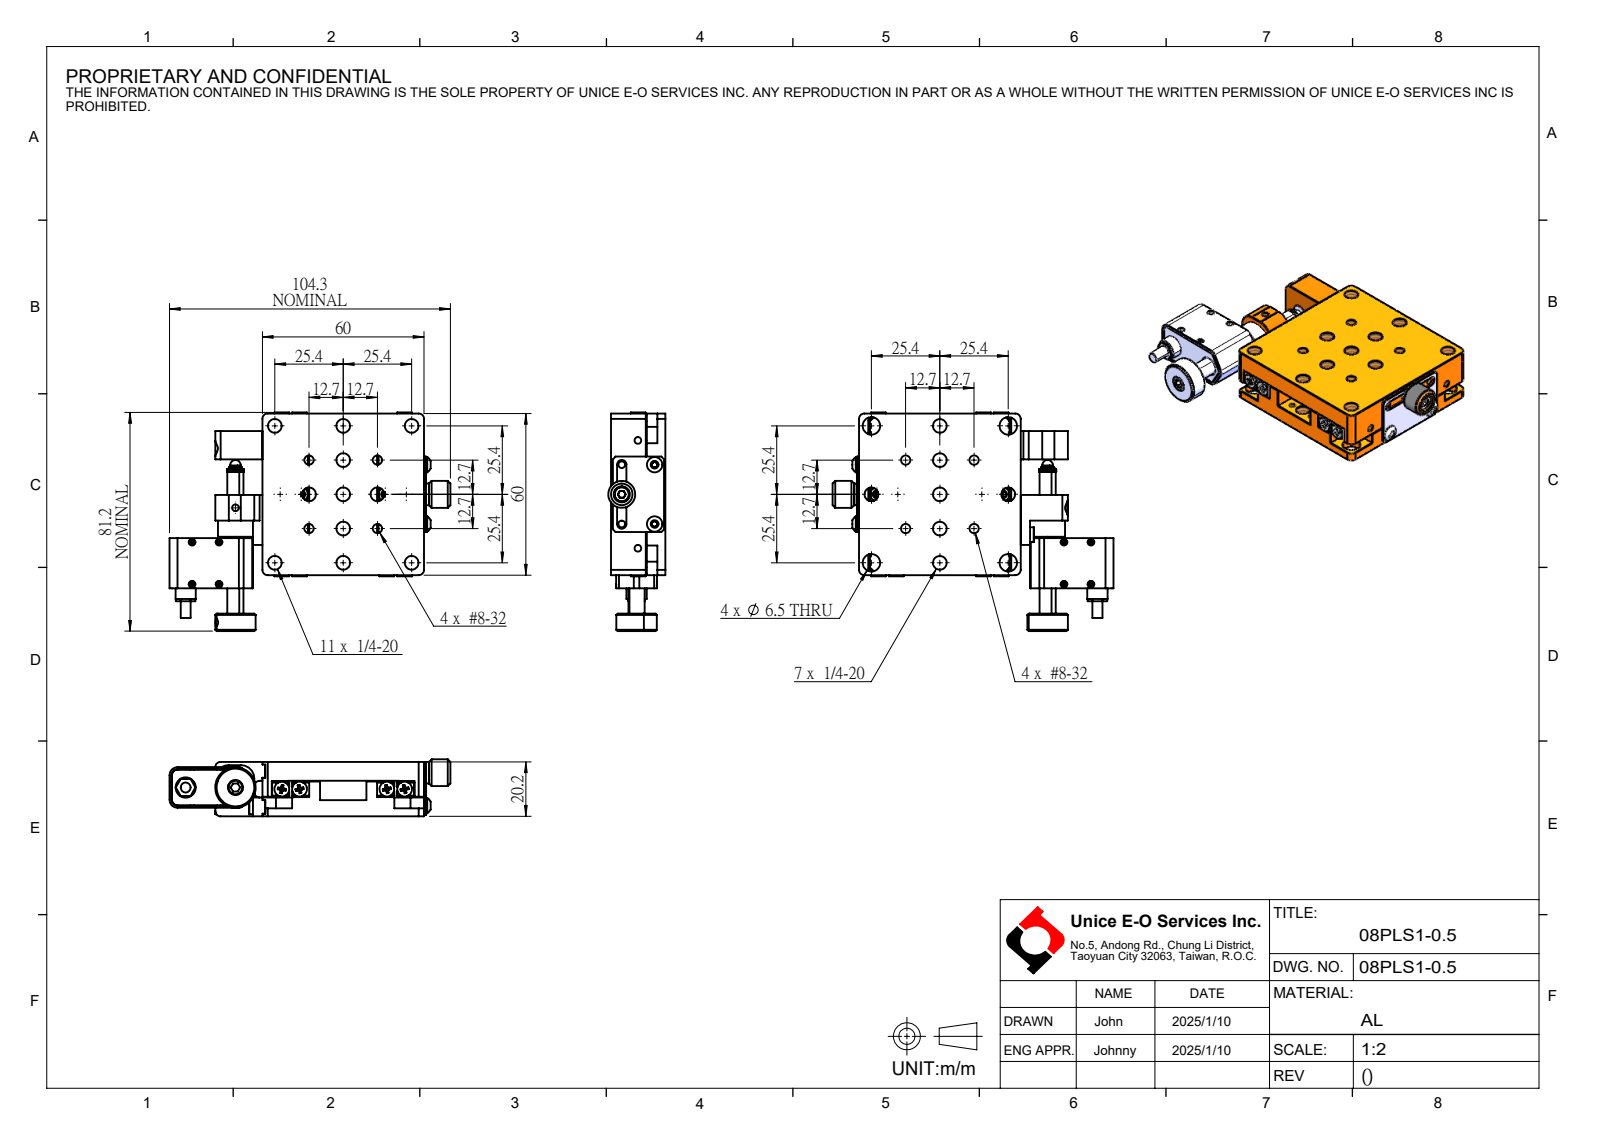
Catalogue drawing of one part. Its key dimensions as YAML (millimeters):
part_name: "08PLS1-0.5"
step_written_by: "SolidWorks 2024 (CONFIG_CONTROL_DESIGN)"
units: millimeters
bodies: {solids: 0, faces: 1785, planar: 652, cylindrical: 504, other: 629}
overall_size: [104.3, 81.17, 21.2]
round_holes:
  - {diameter: 2.05, count: 20}
  - {diameter: 2.5, count: 18}
  - {diameter: 3, count: 13}
  - {diameter: 5, count: 13}
  - {diameter: 5.11, count: 13}
  - {diameter: 6.5, count: 7}
  - {diameter: 3.45, count: 4}
  - {diameter: 3.4, count: 3}
  - {diameter: 1.4, count: 2}
  - {diameter: 2, count: 2}
  - {diameter: 3.2, count: 2}
  - {diameter: 3.5, count: 2}
round_bosses_or_shafts:
  - {diameter: 3, count: 9}
  - {diameter: 5.5, count: 8}
  - {diameter: 6, count: 3}
  - {diameter: 5.7, count: 2}
  - {diameter: 2, count: 2}
  - {diameter: 1.4, count: 2}
  - {diameter: 15, count: 1}
  - {diameter: 10, count: 1}
partial_cylinders:
  - {radius: 2, count: 11}
  - {radius: 5, count: 4}
  - {radius: 6, count: 4}
  - {radius: 1.75, count: 2}
  - {radius: 3, count: 2}
face_to_face_distances: [7.1, 13.1, 20.2, 13.2, 7, 6, 6.1, 0.8, 1, 1.1]
hole_center_spacings: [28.4, 17.96, 25.4, 12.7, 40.16, 20, 35.92, 10]
